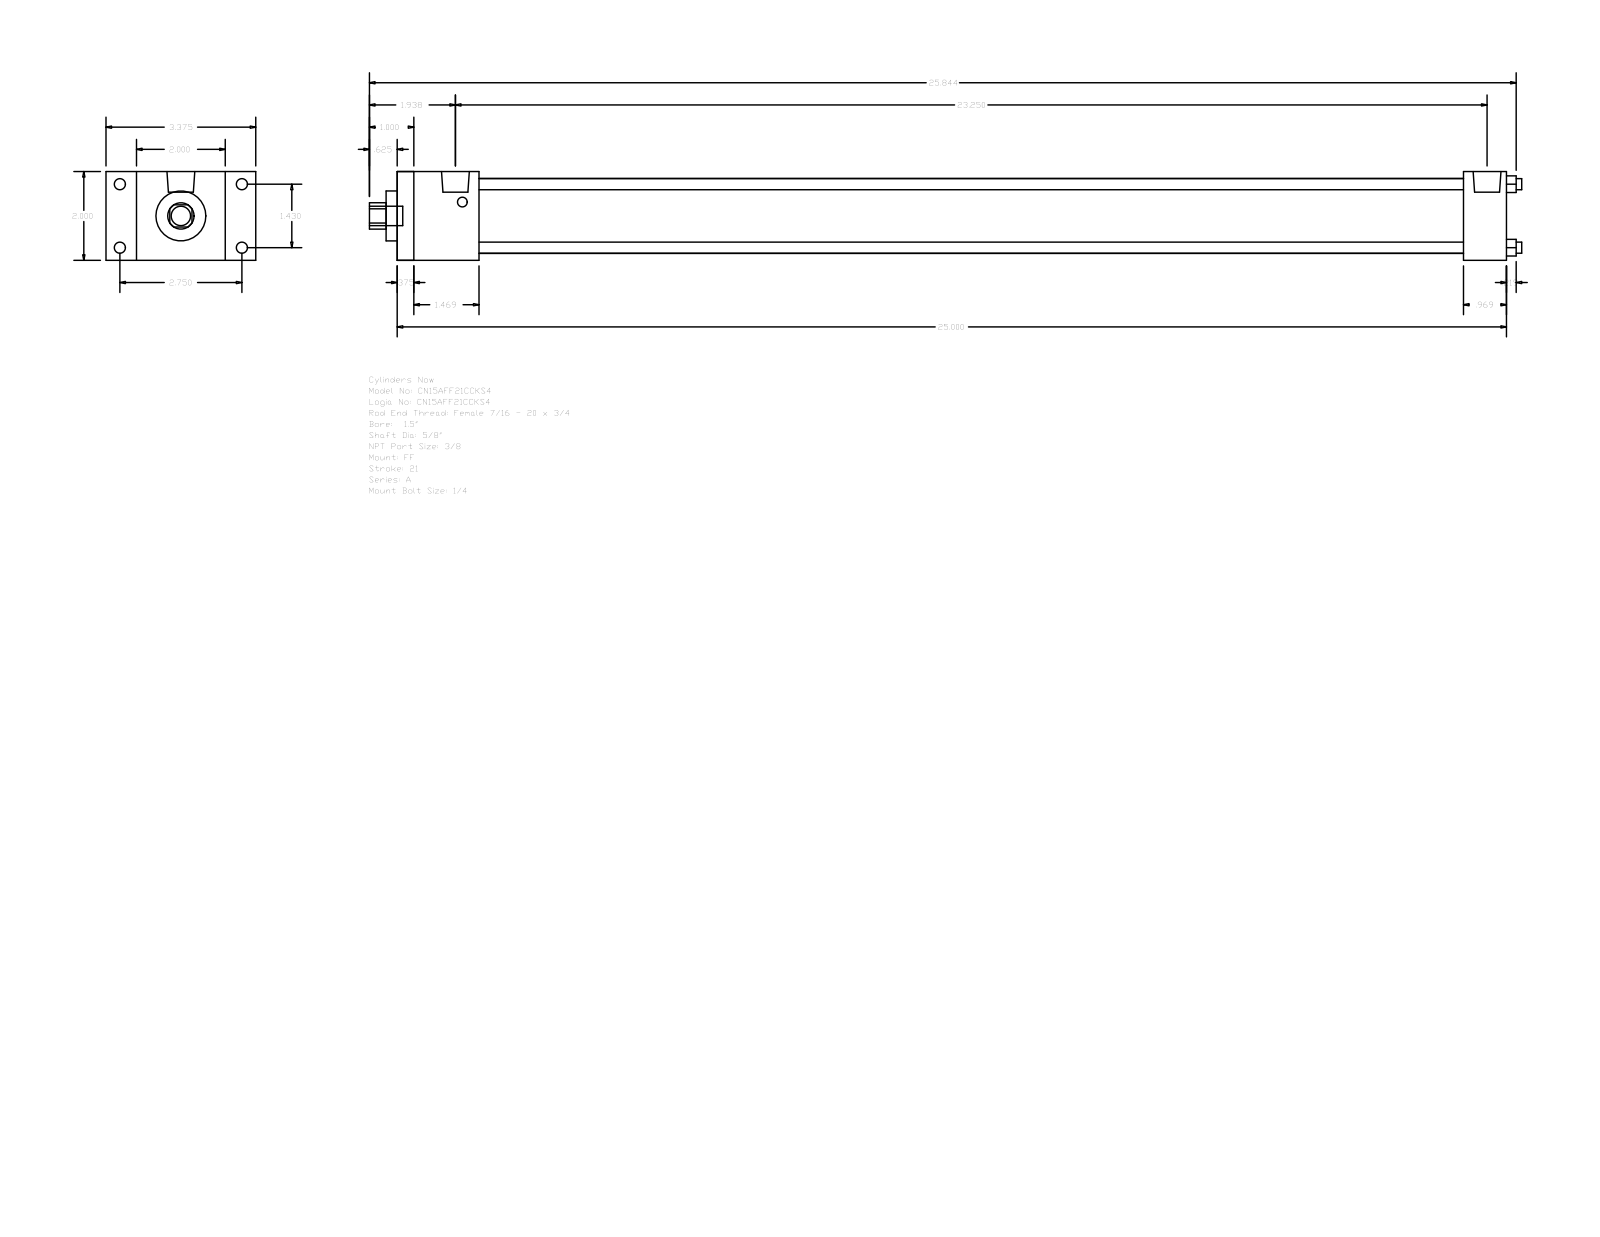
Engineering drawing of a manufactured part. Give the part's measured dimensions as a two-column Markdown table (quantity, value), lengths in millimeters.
| quantity | value |
| --- | --- |
| part name | A_FF__0150_0.625 |
| STEP written by | GSSL Pune (CONFIG_CONTROL_DESIGN) |
| units | millimeters |
| bodies | 0 solids, 92 faces (64 planar, 28 cylindrical, 0 other) |
| overall size | 659.61 × 85.72 × 50.8 |
| round holes (diameter × count) | 6.35 × 4, 15.88 × 1, 28.57 × 1, 42.93 × 1 |
| round bosses / shafts (diameter × count) | 6.35 × 4, 5.56 × 4, 15.93 × 2, 11.11 × 1 |
| partial cylindrical surfaces (radius × count) | 7.54 × 1 |
| main face-to-face distances | 50.8, 635, 9.52, 625.48, 46.83, 610.39, 37.31, 600.87, 563.56, 588.17 |
| hole center spacings | 25.68, 36.32, 51.36 |
